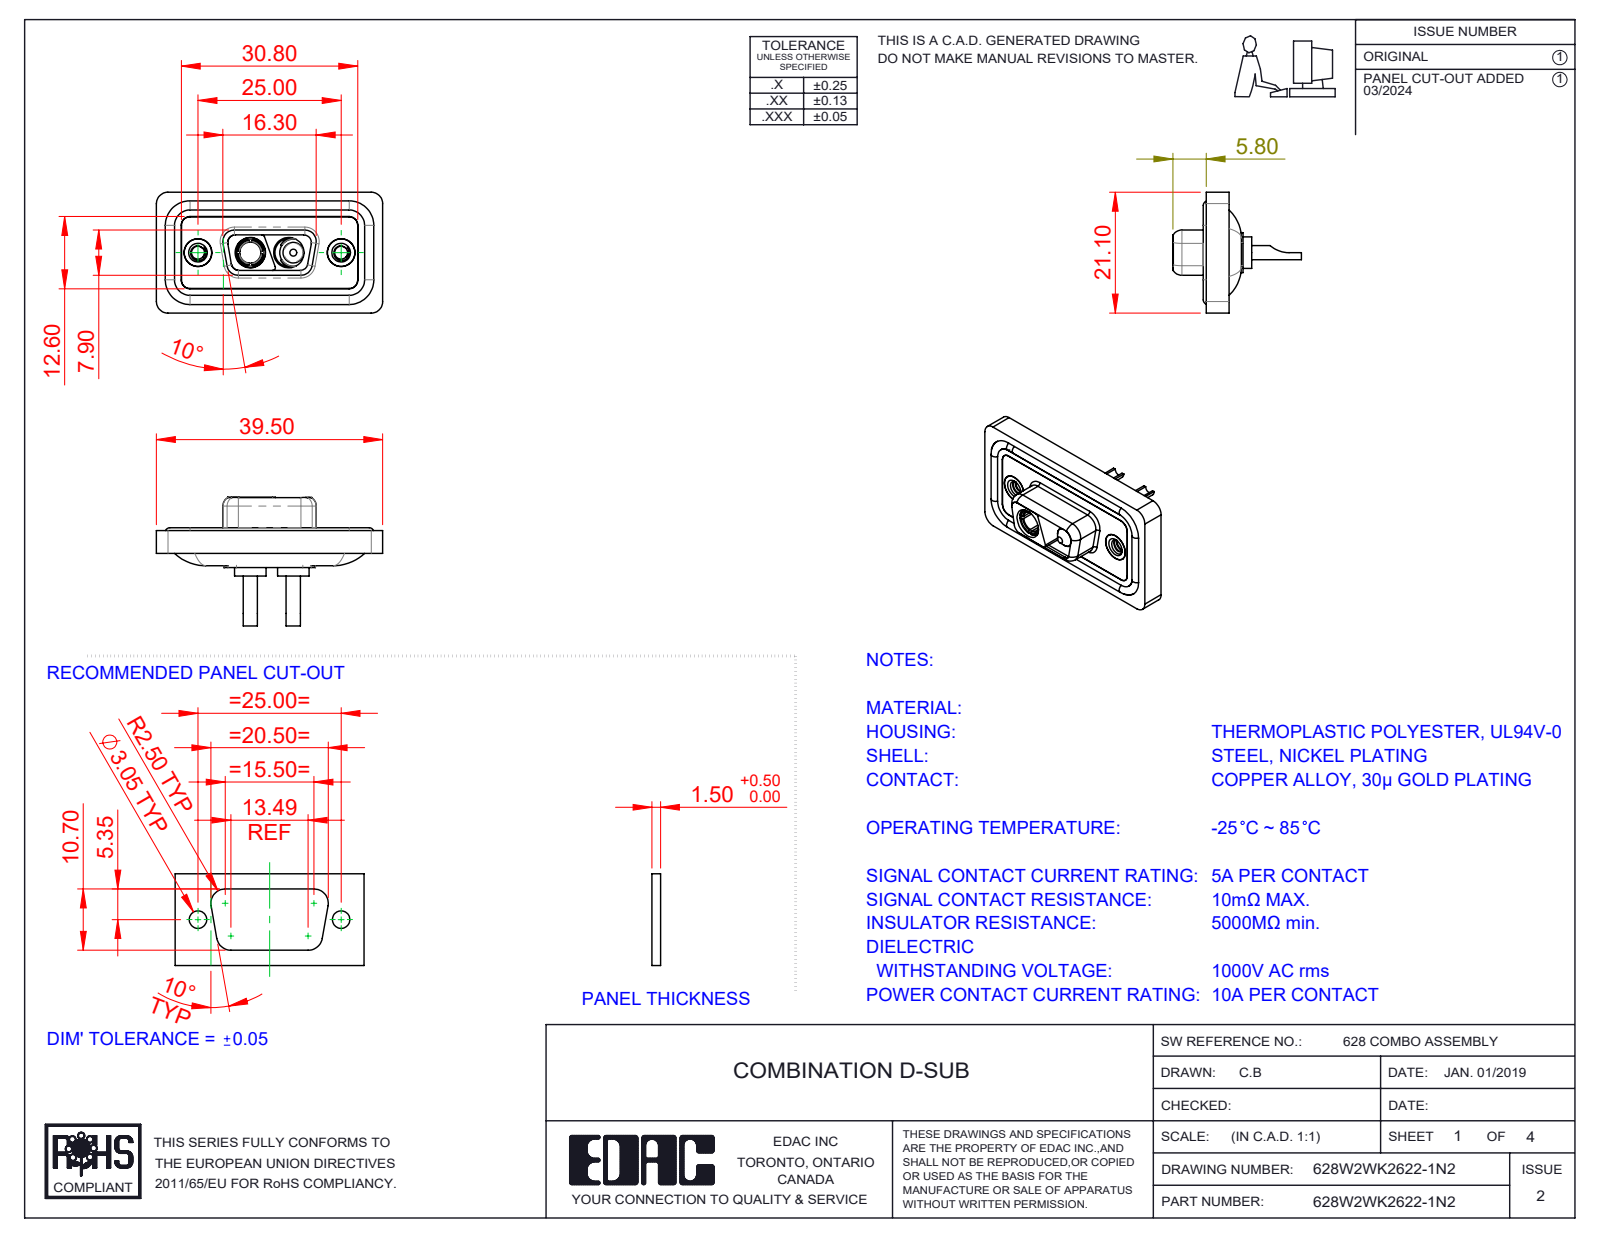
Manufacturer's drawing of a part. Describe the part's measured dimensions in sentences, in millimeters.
The part is named "628Combo Threaded Rivet_2; 628W2WK2622-1N2; Power Pin_10A SC; 628Combo Shell Rear_09 Contacts (+4 more)". Its 3-D file was written by "SolidWorks 2023 (CONFIG_CONTROL_DESIGN)". It is 11 solids with 510 faces: 148 planar, 237 cylindrical and 125 other. Overall it measures 39.5 by 22.45 by 21.1 millimeters. Its volume is 4 597 cubic millimeters and its surface area 7 439 square millimeters. Round holes: 4 of diameter 4.85, 2 of diameter 1.7, 2 of diameter 2.26, 2 of diameter 4, 2 of diameter 4.05, 2 of diameter 5, 2 of diameter 5.3, 1 of diameter 3.7. Round bosses or shafts: 4 of diameter 1.6, 2 of diameter 5.5, 2 of diameter 5.2, 2 of diameter 4.95, 2 of diameter 4.8, 2 of diameter 4.75, 2 of diameter 3.75, 2 of diameter 2.5. Partial cylindrical surfaces (rounded edges, fillets, slot ends): 22 of radius 1.5, 18 of radius 2, 8 of radius 1.35, 8 of radius 1.6, 6 of radius 0.5, 4 of radius 0.25, 4 of radius 0.6, 4 of radius 0.65. The main face-to-face distances are 0.4, 1.1, 2.9, 1.6, 0.5, 1.8, 5.65, 1.5, 5.35, 3.1. The hole center spacings are 9.14, 15.86, 6.72, 25.
